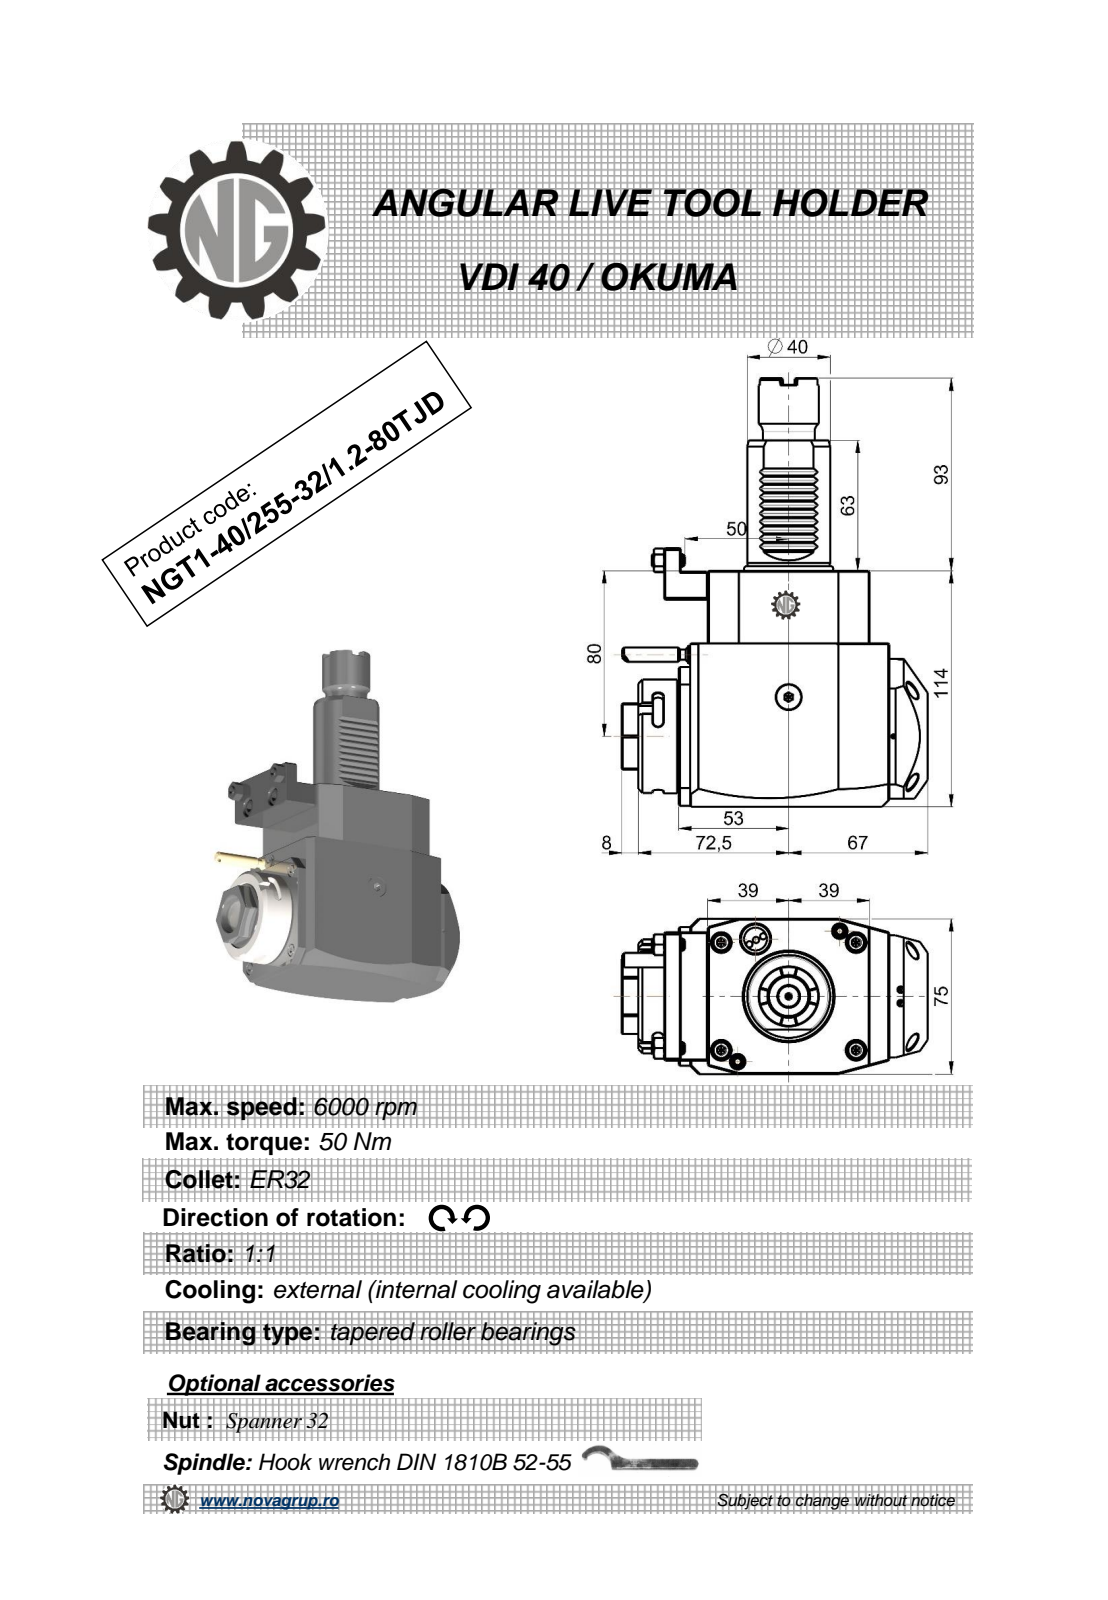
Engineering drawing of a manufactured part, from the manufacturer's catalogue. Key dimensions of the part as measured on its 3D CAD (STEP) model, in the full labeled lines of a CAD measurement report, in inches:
Part name (STEP PRODUCT): NGT1_40_255_32_1_2_80TJD
STEP written by: PRO/ENGINEER BY PARAMETRIC TECHNOLOGY CORPORATION, 2010280 (CONFIG_CONTROL_DESIGN)
Units: inches
Bodies: 1 solid, 398 faces (200 planar, 70 cylindrical, 128 other)
Overall size (bounding box): 8.15 × 5.807 × 2.953
Volume: 60.7 in³ · Surface area: 118.3 in²
Round holes (diameter × count): ⌀0.098 ×1, ⌀0.118 ×1, ⌀0.906 ×1
Round bosses / shafts (diameter × count): ⌀0.236 ×2, ⌀2.165 ×1, ⌀1.89 ×1, ⌀1.575 ×1, ⌀1.142 ×1, ⌀0.984 ×1, ⌀0.353 ×1, ⌀0.276 ×1
Partial cylindrical surfaces — rounded edges, fillets, slot ends (radius × count): R0.012 ×10, R0.012 ×10, R0.098 ×6, R7.087 ×2, R0.02 ×1, R0.394 ×1, R0.965 ×1, R1.476 ×1
Main face-to-face distances: 2.953, 4.488, 0.551, 0.827, 3.622, 0.492, 0.02, 0.768, 4.39, 0.276
Hole centre spacings: 1.701
